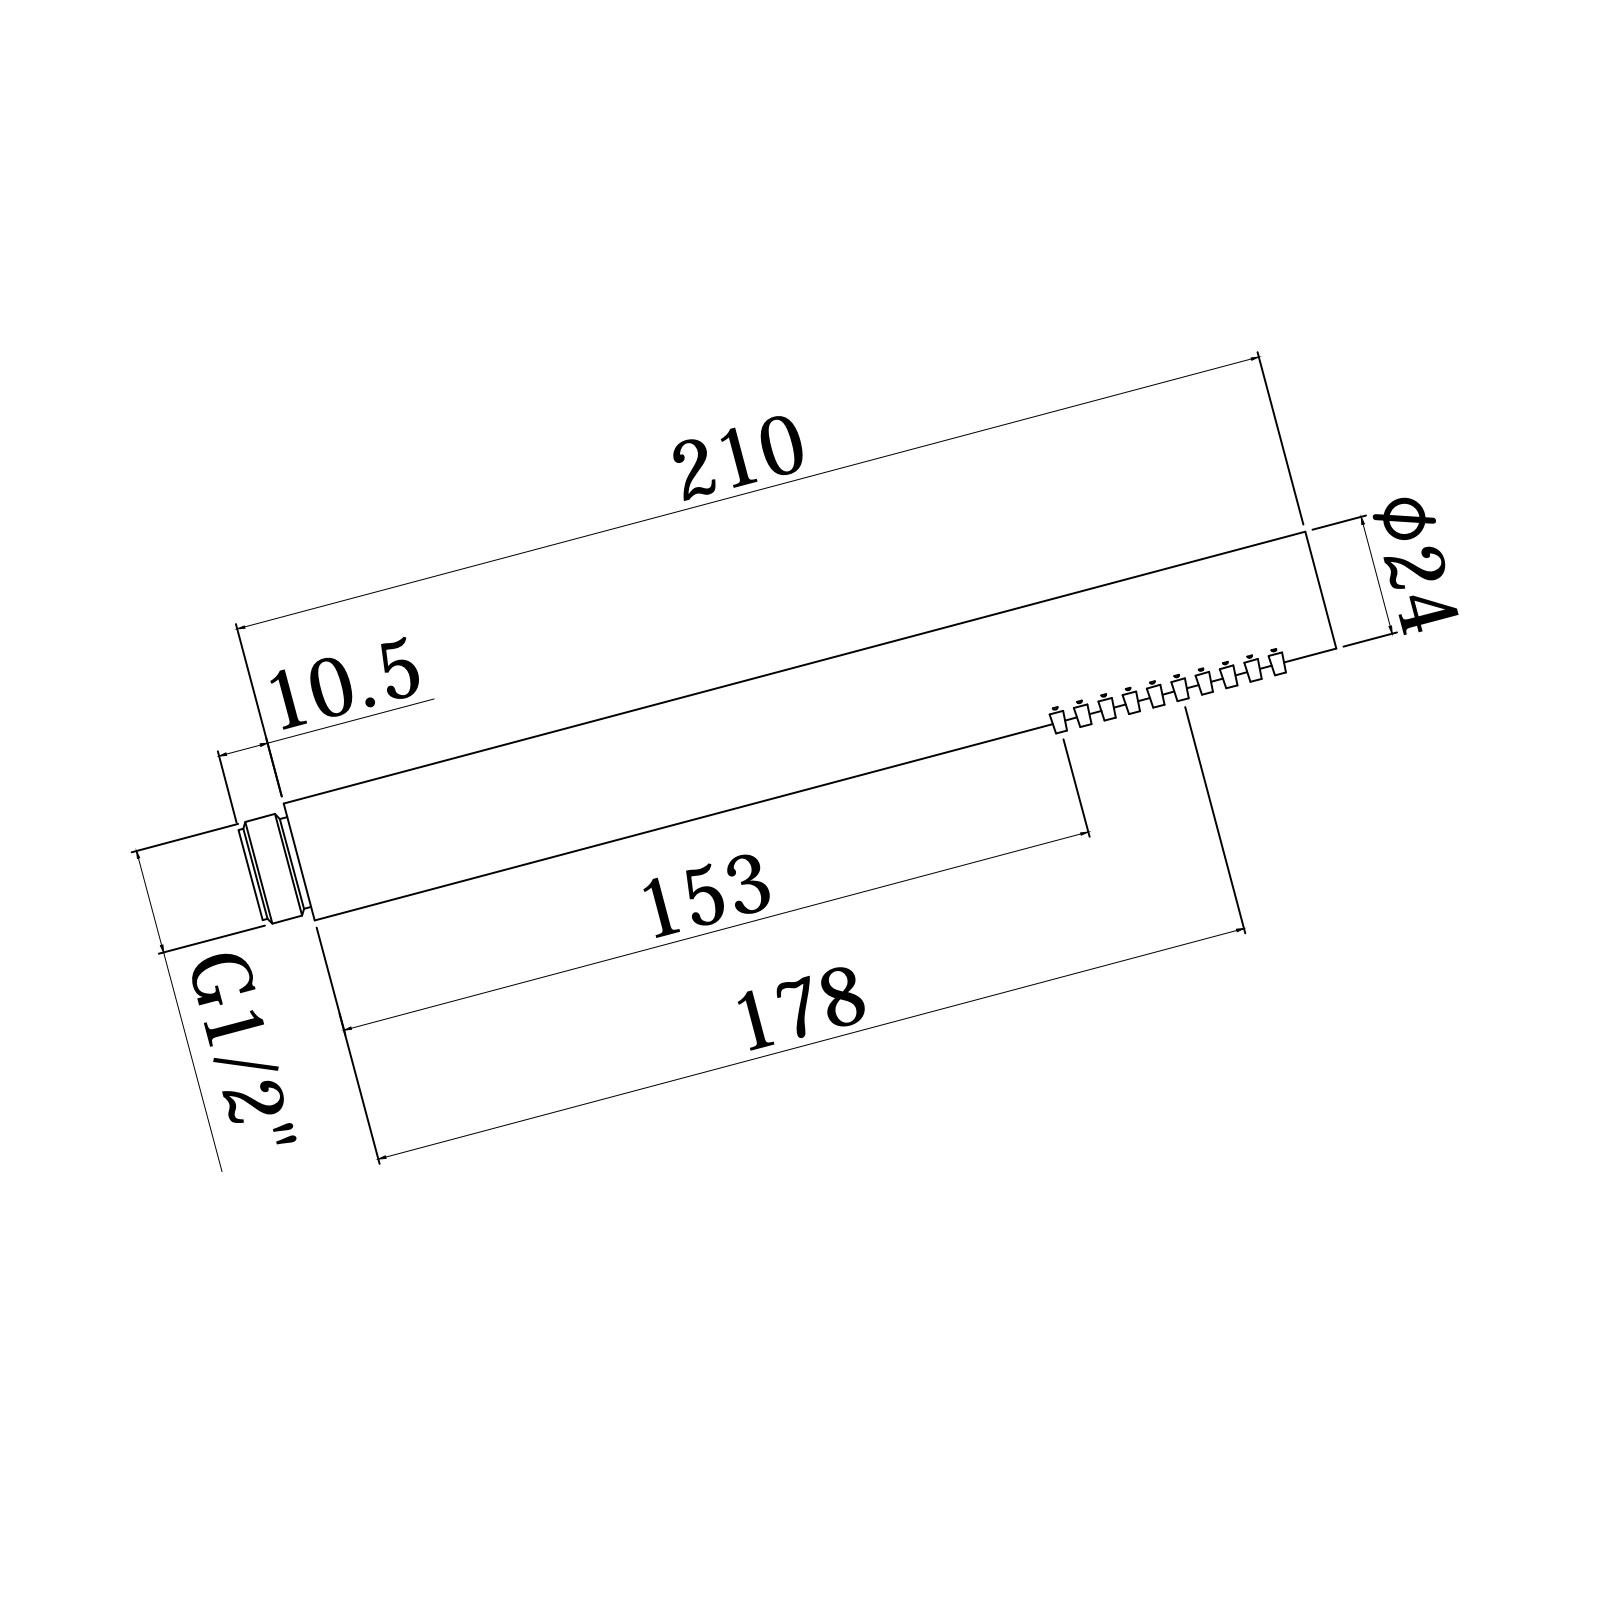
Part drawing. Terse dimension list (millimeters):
name: ZDOC067CR
written by: CREO PARAMETRIC BY PTC INC, 2020044 (CONFIG_CONTROL_DESIGN)
unit: mm
bodies: 0 solids, 299 faces (95 planar, 100 cylindrical, 104 other)
size: 220 × 26 × 24
holes: 28× ⌀1, 1× ⌀14.5, 1× ⌀20
bosses: 1× ⌀24, 1× ⌀20.9, 1× ⌀18.5
rounds: 12× R0.5
face distances: 3, 207, 210, 4, 10, 217, 220, 1, 5
hole spacings: 5, 10, 9.43, 12.81, 6.4, 10.77, 13, 15
